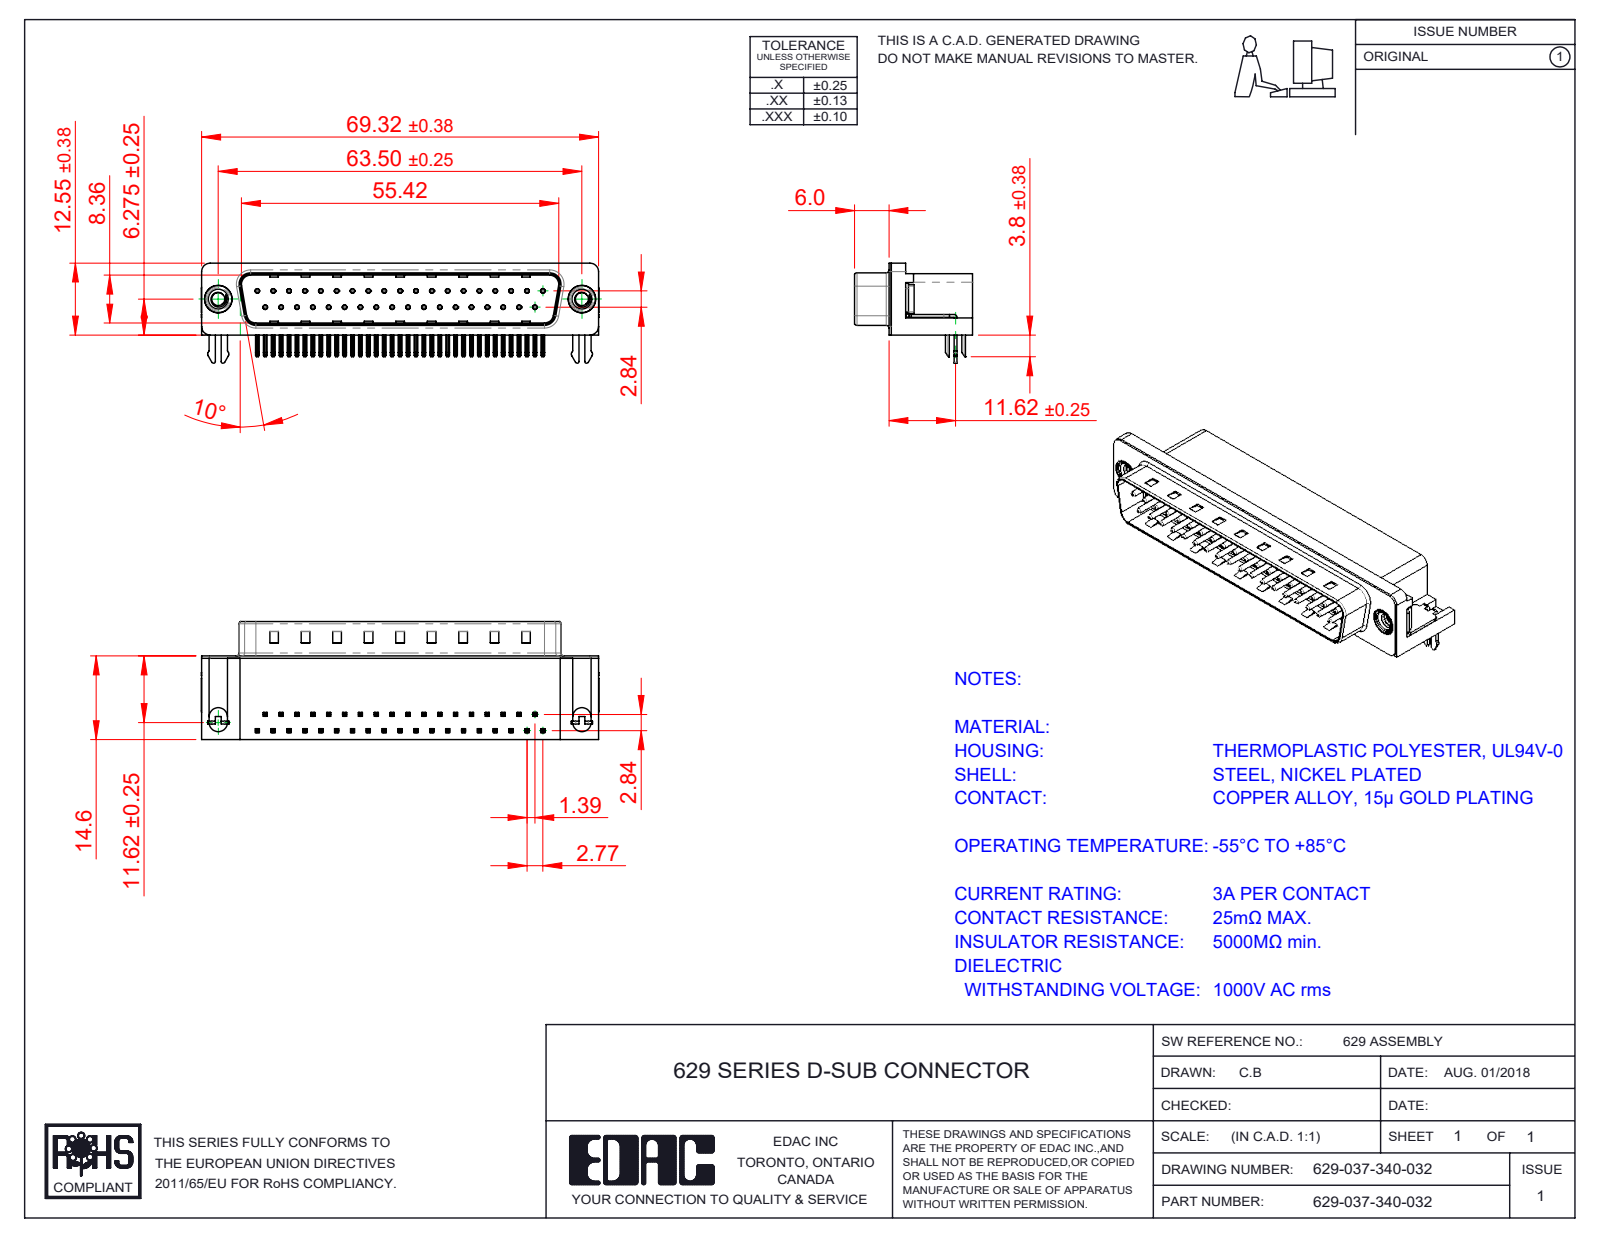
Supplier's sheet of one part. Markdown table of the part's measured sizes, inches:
| quantity | value |
| --- | --- |
| part name | 629 2 Prong Board Lock; 629-037-340-032; 629 4-40 Threaded Rivet; 629 Housing_37 Socket (+3 more) |
| STEP written by | SolidWorks 2020 (CONFIG_CONTROL_DESIGN) |
| units | inches |
| bodies | 43 solids, 3237 faces (2043 planar, 923 cylindrical, 271 other) |
| overall size | 2.732 × 0.811 × 0.688 |
| volume | 0.608 in³ |
| surface area | 16.79 in² |
| round holes (diameter × count) | 0.014 × 37, 0.031 × 37, 0.089 × 2, 0.157 × 2, 0.189 × 2, 0.197 × 2 |
| round bosses / shafts (diameter × count) | 0.03 × 37, 0.193 × 2, 0.187 × 2, 0.154 × 2 |
| partial cylindrical surfaces (radius × count) | 0.01 × 156, 0.005 × 74, 0.039 × 16, 0.02 × 14, 0.063 × 8, 0.059 × 7, 0.013 × 4, 0.035 × 4 |
| main face-to-face distances | 0.016, 0.407, 0.559, 0.345, 0.083, 0.067, 0.412, 0.428, 0.575, 0.053 |
| hole center spacings | 0.109, 0.124, 0.218, 0.327, 0.436, 0.545, 0.654, 0.763 |
